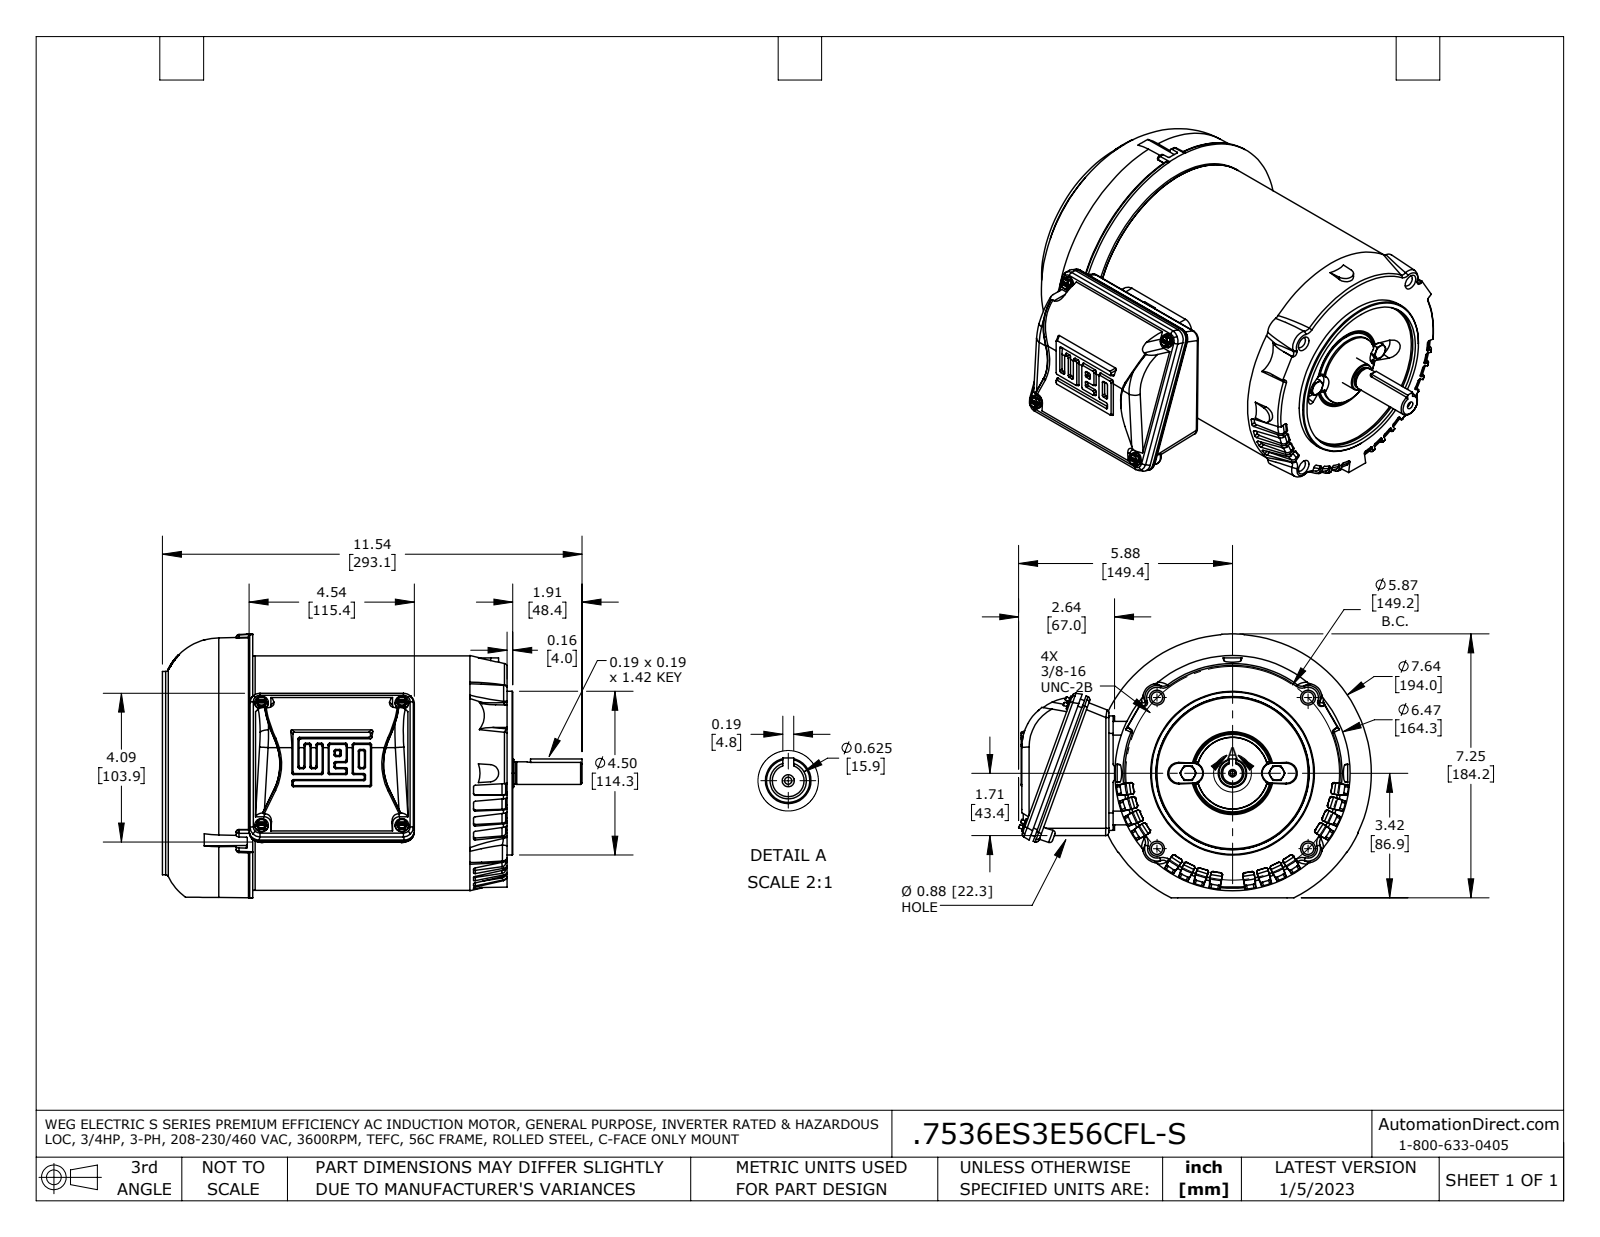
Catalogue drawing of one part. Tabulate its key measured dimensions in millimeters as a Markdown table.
| quantity | value |
| --- | --- |
| part name | 56C_3PH_TEFC_GP_11535_FL fxt |
| STEP written by | SolidWorks 2021 (AUTOMOTIVE_DESIGN) |
| units | millimeters |
| bodies | 13 solids, 1283 faces (471 planar, 275 cylindrical, 537 other) |
| overall size | 293.1 × 246.4 × 191.8 |
| volume | 5 834 000 mm³ |
| surface area | 380 100 mm² |
| round holes (diameter × count) | 8 × 4, 3.1 × 1 |
| round bosses / shafts (diameter × count) | 9.5 × 4, 8.9 × 2, 163.8 × 1, 163.8 × 1, 142 × 1, 114.3 × 1, 19.9 × 1, 15.9 × 1 |
| partial cylindrical surfaces (radius × count) | 1.2 × 40, 0.2 × 38, 1.3 × 32, 1.5 × 12, 2.2 × 12, 0.5 × 10, 5.2 × 8, 7 × 8 |
| main face-to-face distances | 150, 1.7, 151.7, 58, 59.7, 209.7, 235.7, 177.7, 176, 26 |
| hole center spacings | 74.6, 105.5, 149.2 |
